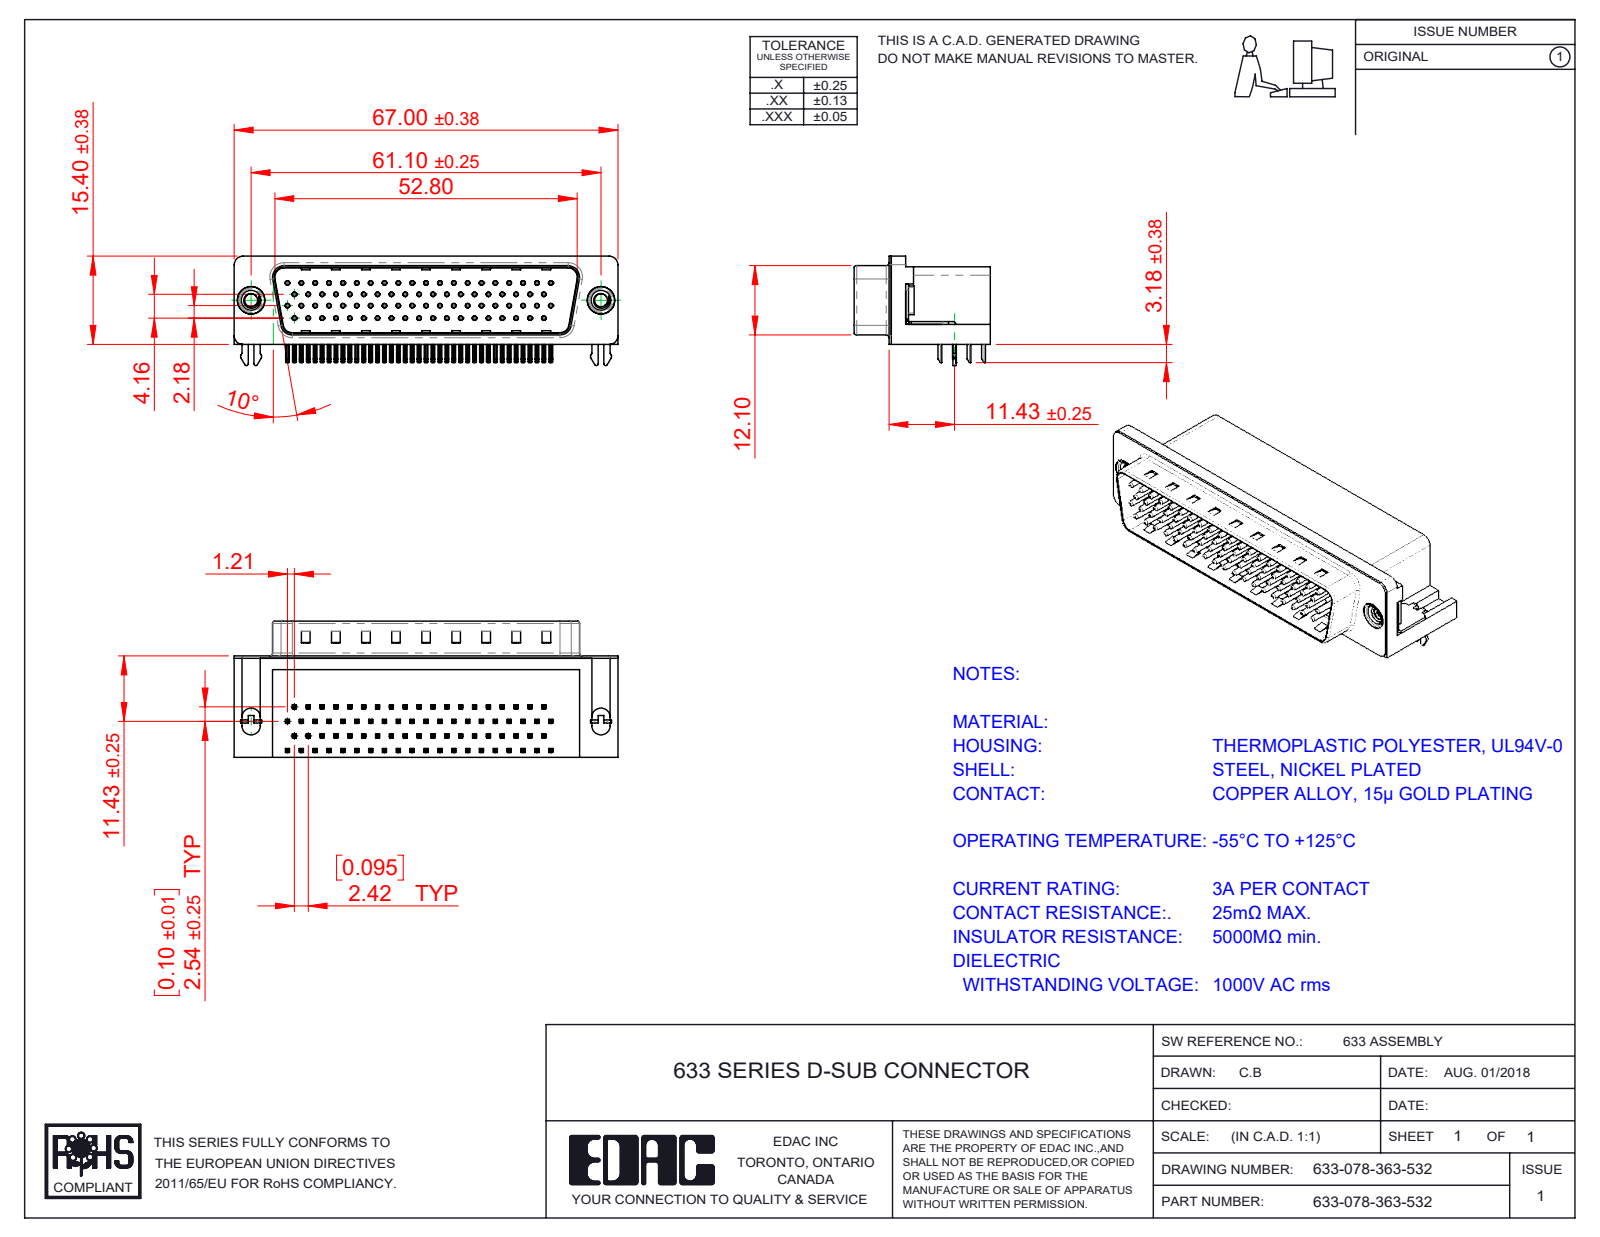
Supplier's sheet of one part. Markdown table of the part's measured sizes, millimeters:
| quantity | value |
| --- | --- |
| part name | 633 2 Prong Board Lock_78 Contact; 633 Housing_78 Contact; 633 Contact Bottom_78 Contact; 633 Contact Middle_78 Contact (+5 more) |
| STEP written by | SolidWorks 2016 (CONFIG_CONTROL_DESIGN) |
| units | millimeters |
| bodies | 84 solids, 6316 faces (4013 planar, 1786 cylindrical, 517 other) |
| overall size | 67 × 23.8 × 19.1 |
| volume | 14 614 mm³ |
| surface area | 16 358 mm² |
| round holes (diameter × count) | 0.35 × 78, 0.8 × 78, 2.26 × 2, 4 × 2, 4.8 × 2, 5 × 2 |
| round bosses / shafts (diameter × count) | 0.75 × 78, 4.9 × 2, 4.75 × 2, 3.9 × 2 |
| partial cylindrical surfaces (radius × count) | 0.25 × 320, 0.12 × 156, 1 × 16, 0.5 × 14, 1.6 × 8, 1.5 × 6, 0.32 × 4, 0.45 × 4 |
| main face-to-face distances | 0.4, 13.2, 17.3, 11.7, 13.35, 2.05, 13.75, 1.65, 1.85, 11.9 |
| hole center spacings | 2.42, 4.84, 7.26, 9.68, 6.26, 7.13, 12.1, 8.62 |
